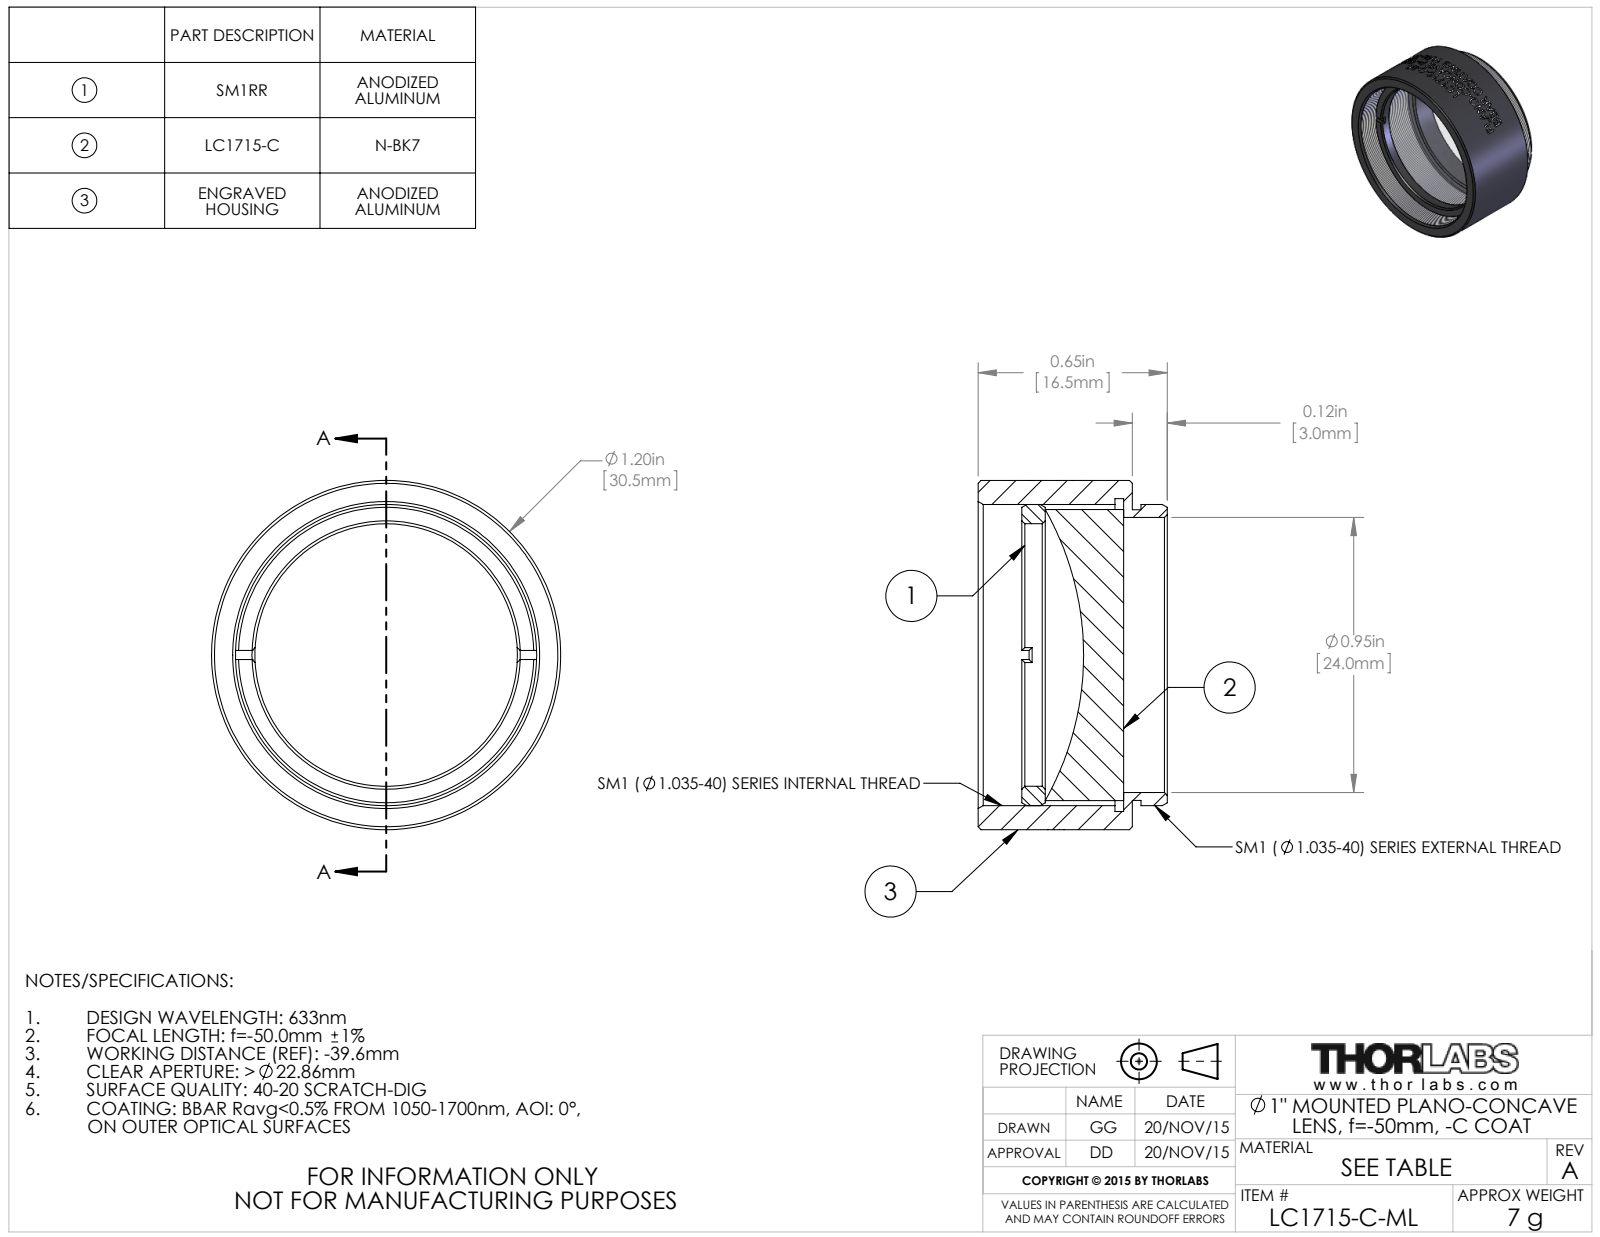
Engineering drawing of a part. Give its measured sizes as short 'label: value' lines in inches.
name: TTN045284-E0W
written by: SolidWorks 2014 (CONFIG_CONTROL_DESIGN)
unit: in
bodies: 3 solids, 151 faces (20 planar, 107 cylindrical, 24 other)
size: 1.2 × 1.2 × 0.65
volume: 0.344 in³; area: 8.744 in²
holes: 1× ⌀0.902, 1× ⌀0.945, 1× ⌀1.075
bosses: 1× ⌀1.2, 1× ⌀1.035, 1× ⌀1, 1× ⌀0.999
face distances: 0.03, 0.03, 0.5, 0.53, 0.5, 0.15, 0.3, 0.27, 0.27, 0.23
